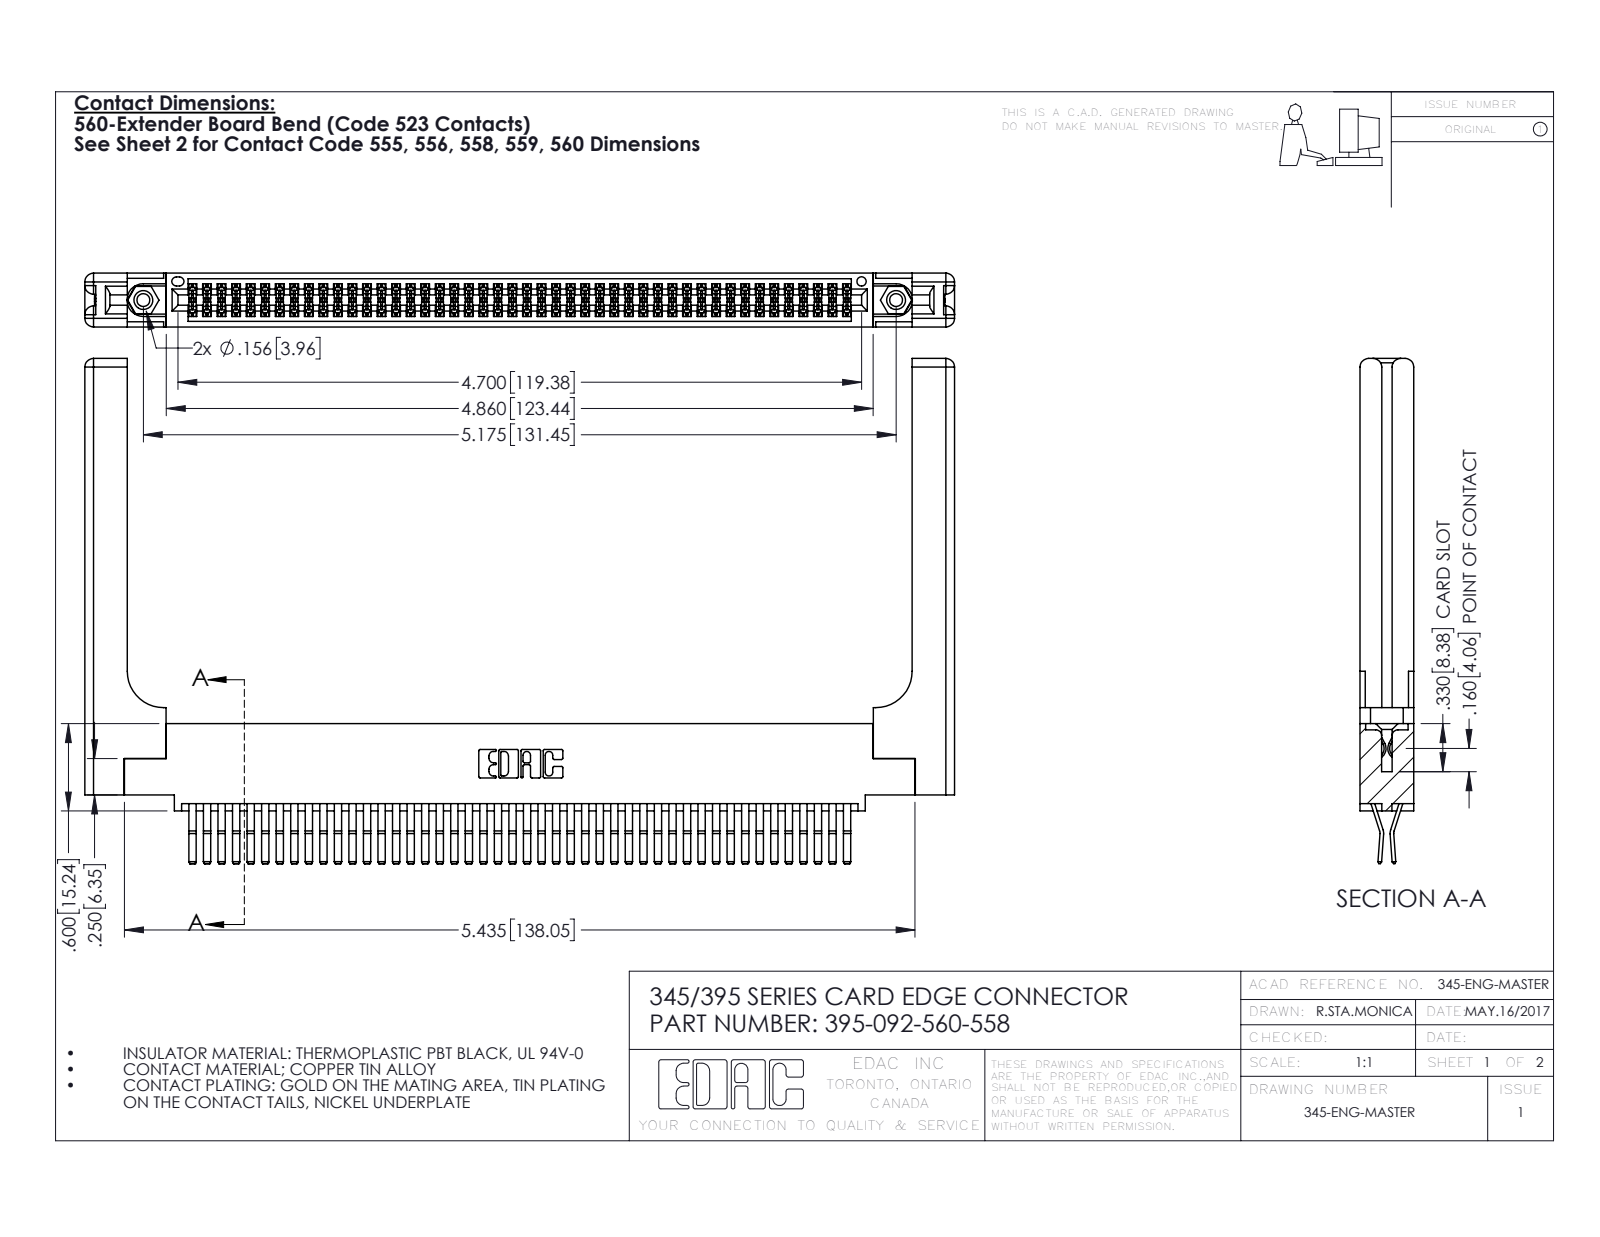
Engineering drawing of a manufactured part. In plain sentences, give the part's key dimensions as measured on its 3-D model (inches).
The part is named "395-092-560-558; 345 Part_0.110 Offset - 0.156 Dia-TH; 345-250-001_345-250-001-102; 345-220-058_345-220-058 (+1 more)". Its 3-D file was written by "SolidWorks 2016 (CONFIG_CONTROL_DESIGN)". It is 97 solids with 5170 faces: 3268 planar, 1842 cylindrical and 60 other. Overall it measures 5.979 by 3.472 by 0.37 inches. Its volume is 1.452 cubic inches and its surface area 45.61 square inches. Round holes: 2 of diameter 0.089, 2 of diameter 0.125, 2 of diameter 0.156, 1 of diameter 0.064. Round bosses or shafts: 2 of diameter 0.155. Partial cylindrical surfaces (rounded edges, fillets, slot ends): 138 of radius 0.006, 22 of radius 0.01, 16 of radius 0.06, 6 of radius 0.007, 6 of radius 0.031, 3 of radius 0.026, 2 of radius 0.01, 2 of radius 0.014. The main face-to-face distances are 0.072, 0.37, 0.298, 0.025, 0.2, 0.098, 0.272, 0.225, 0.148, 0.15. The hole center spacings are 0.27, 4.939, 5.175.
